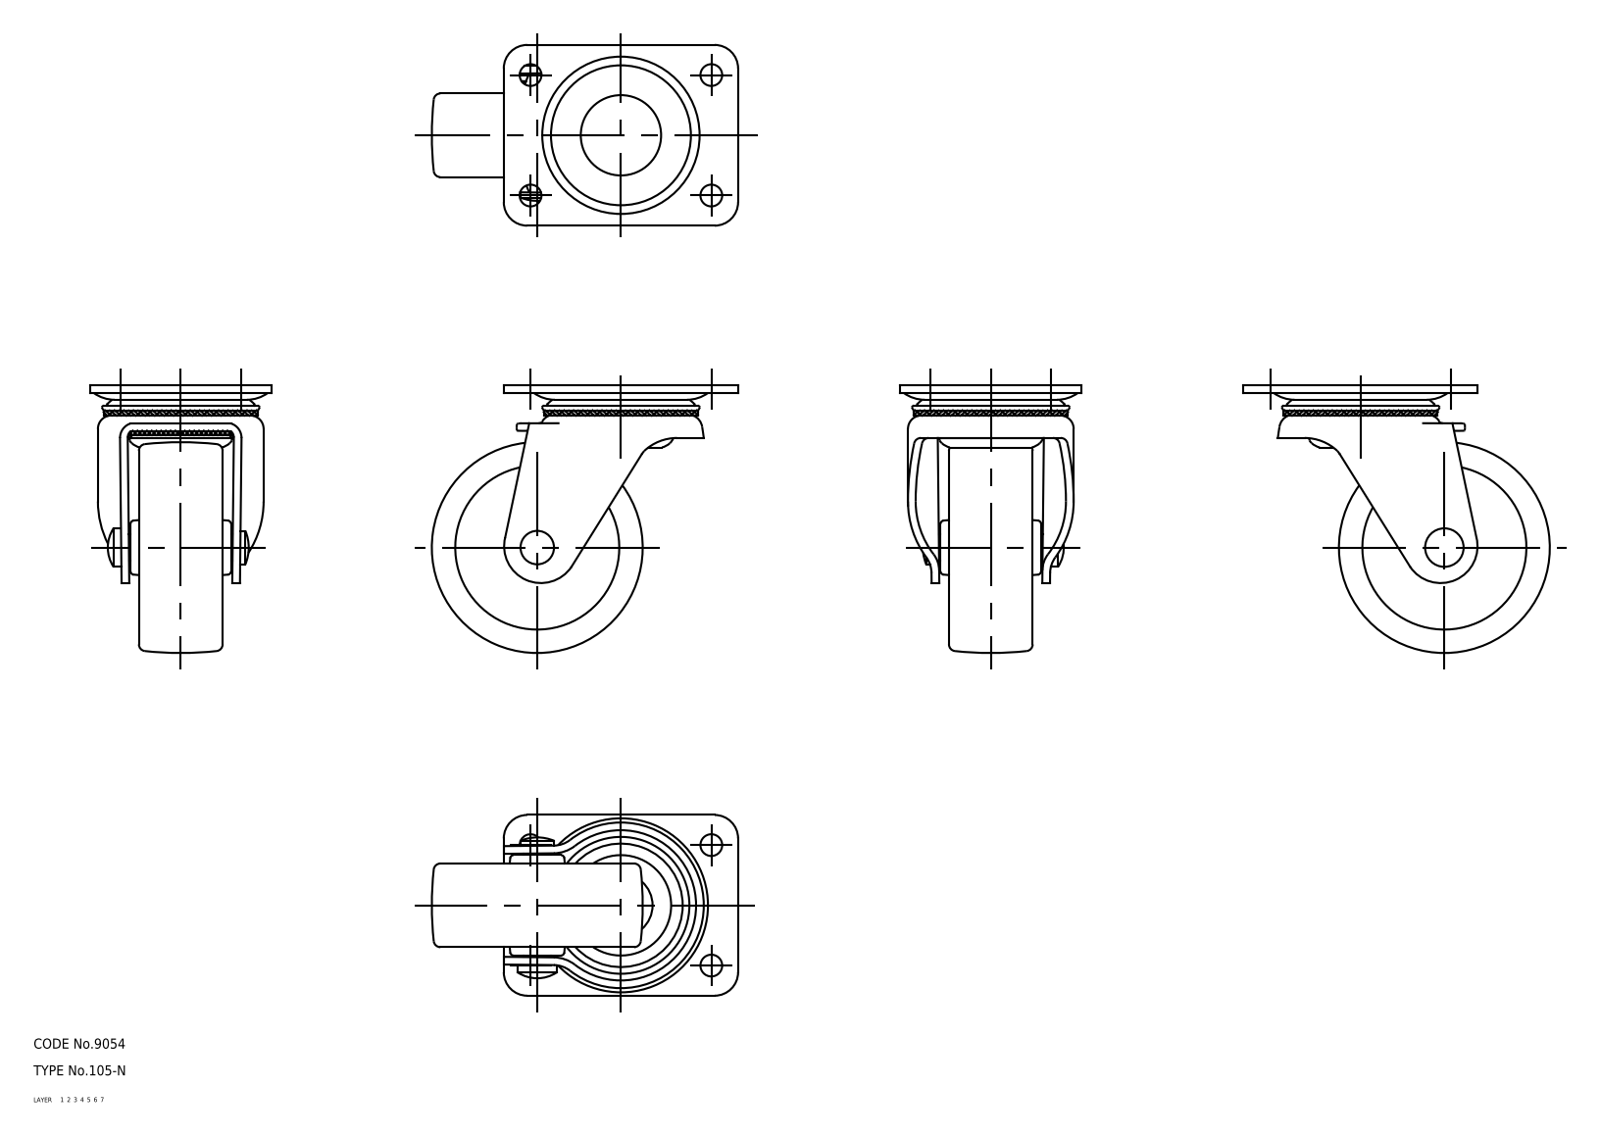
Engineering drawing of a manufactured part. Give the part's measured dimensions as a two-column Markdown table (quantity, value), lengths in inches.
| quantity | value |
| --- | --- |
| part name | wheel; axle; mounting plate; main shaft (+1 more) |
| STEP written by | CADfix (AUTOMOTIVE_DESIGN) |
| units | inches |
| bodies | 5 solids, 231 faces (0 planar, 0 cylindrical, 231 other) |
| overall size | 3.602 × 3.15 × 2.126 |
| volume | 5.374 in³ |
| surface area | 59.13 in² |
